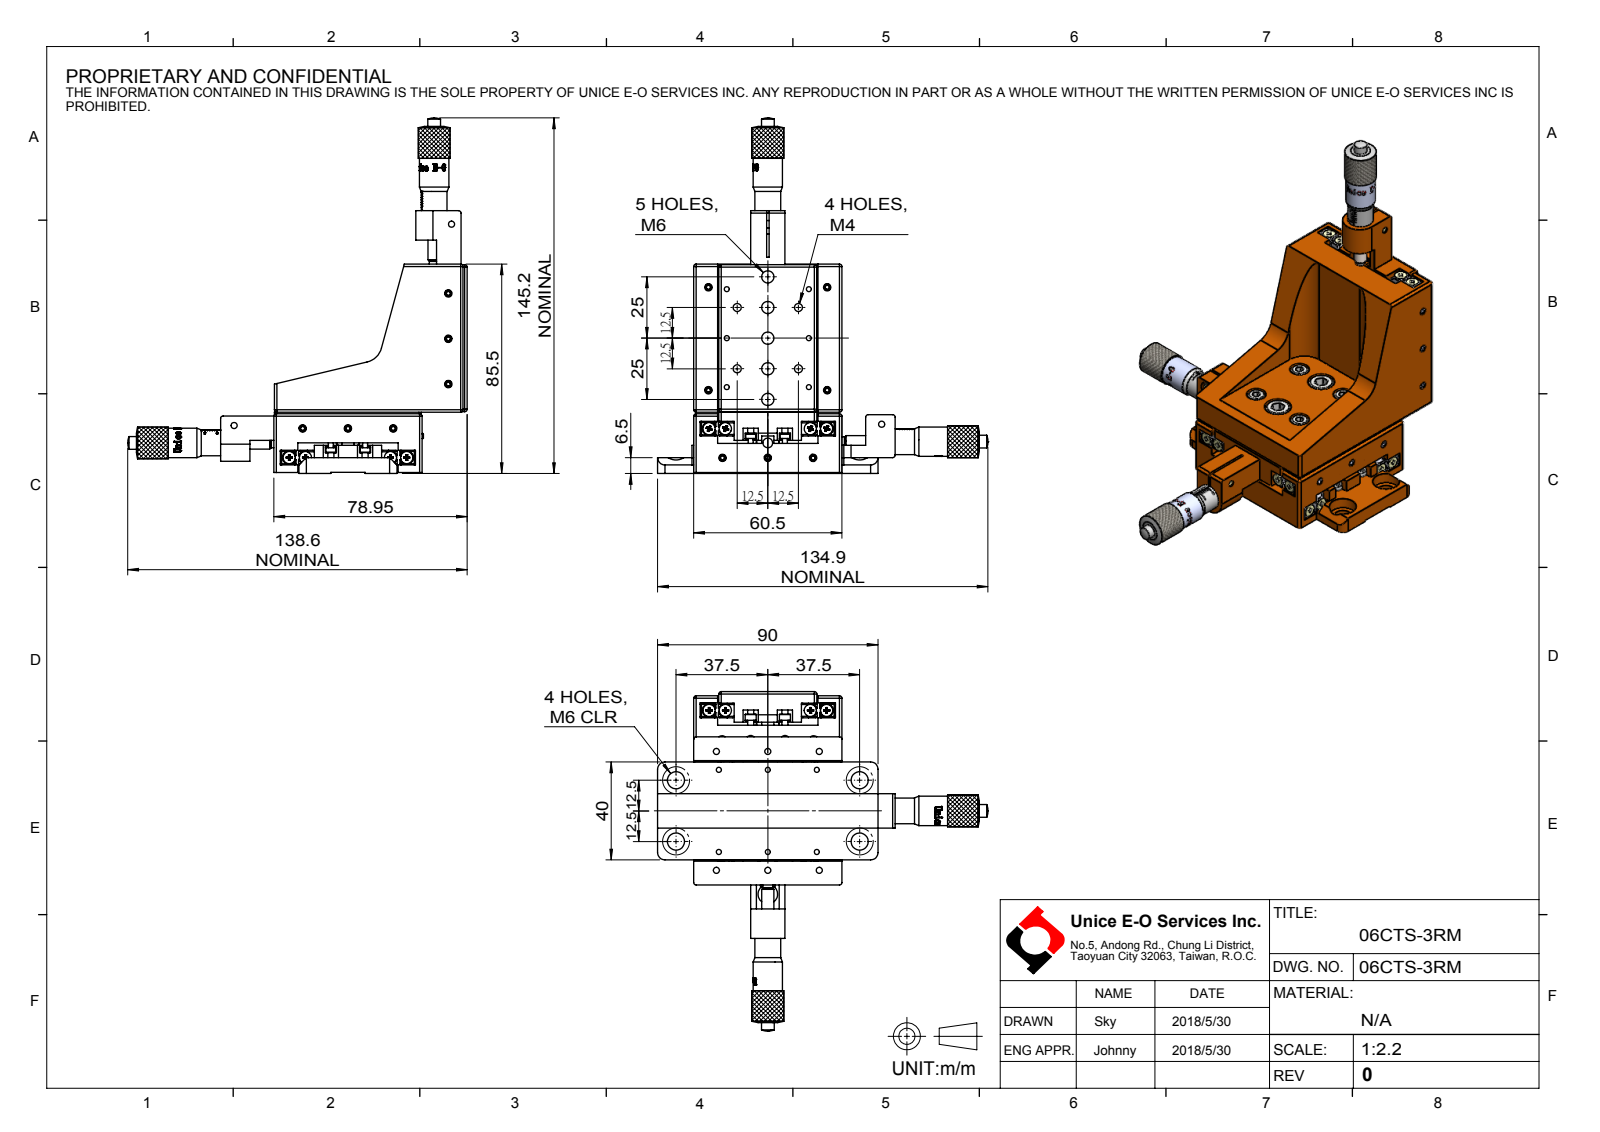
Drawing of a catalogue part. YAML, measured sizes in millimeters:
part_name: "06CTS-3RM"
step_written_by: "SolidWorks 2016 (AUTOMOTIVE_DESIGN)"
units: millimeters
bodies: {solids: 0, faces: 1304, planar: 793, cylindrical: 342, other: 169}
overall_size: [145.15, 138.6, 134.9]
round_holes:
  - {diameter: 2.05, count: 12}
  - {diameter: 2.5, count: 9}
  - {diameter: 8, count: 6}
  - {diameter: 11, count: 6}
  - {diameter: 5, count: 5}
  - {diameter: 3.3, count: 4}
  - {diameter: 7, count: 4}
  - {diameter: 6.5, count: 3}
  - {diameter: 9.5, count: 3}
  - {diameter: 1.6, count: 2}
  - {diameter: 4, count: 1}
round_bosses_or_shafts:
  - {diameter: 5, count: 15}
  - {diameter: 4, count: 6}
  - {diameter: 7, count: 4}
  - {diameter: 2, count: 4}
  - {diameter: 13, count: 3}
  - {diameter: 12, count: 3}
  - {diameter: 10.5, count: 3}
  - {diameter: 5.2, count: 3}
partial_cylinders:
  - {radius: 1, count: 38}
  - {radius: 3, count: 6}
  - {radius: 1.5, count: 4}
  - {radius: 5.98, count: 3}
  - {radius: 2, count: 2}
  - {radius: 7, count: 2}
  - {radius: 8.5, count: 2}
  - {radius: 8, count: 1}
face_to_face_distances: [3, 6, 9, 16.5, 60.5, 12.5, 3.1, 12, 6.75, 11.8]
hole_center_spacings: [25, 12.5, 8.62, 13.2, 17.68, 20, 27.95, 30.2]
